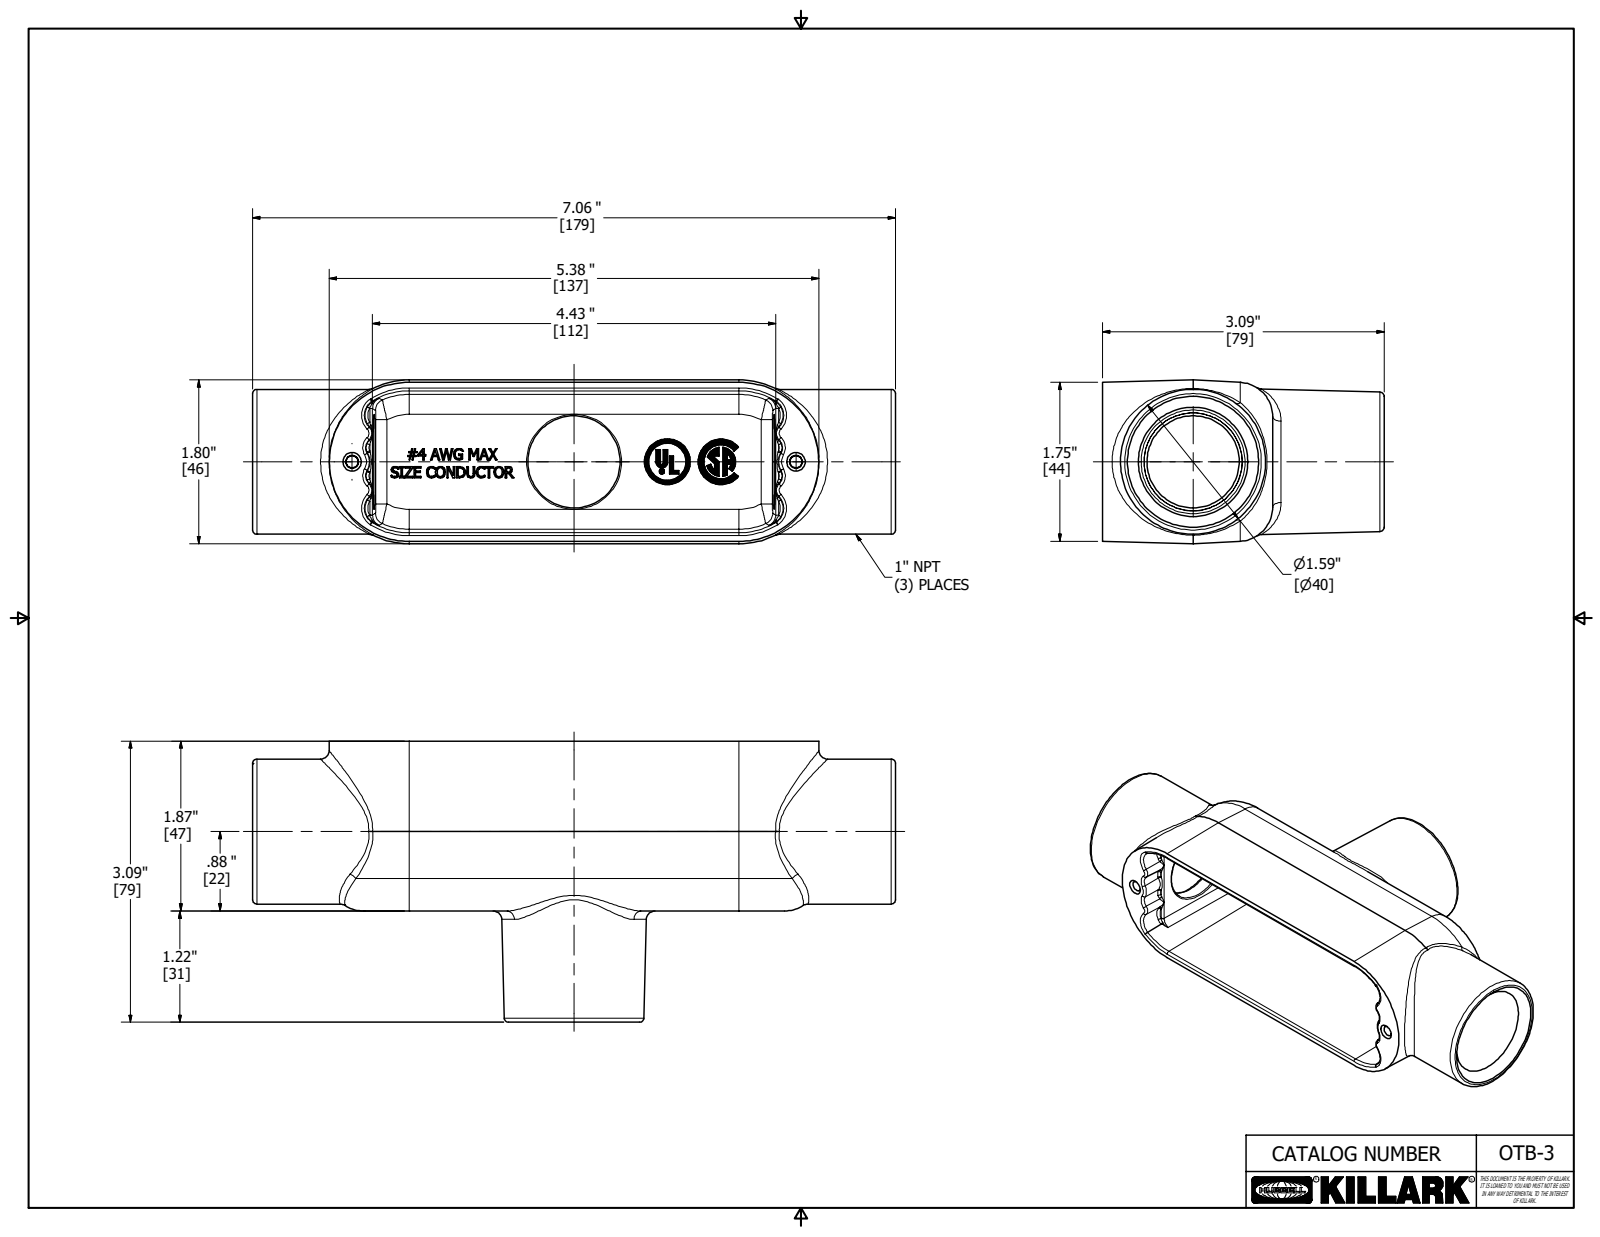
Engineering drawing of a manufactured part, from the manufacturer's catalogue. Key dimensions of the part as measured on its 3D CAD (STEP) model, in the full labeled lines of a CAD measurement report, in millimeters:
Part name (STEP PRODUCT): 12129-1
STEP written by: Autodesk Inventor 2018 (AUTOMOTIVE_DESIGN)
Units: millimetres
Bodies: 1 solid, 778 faces (421 planar, 45 cylindrical, 312 other)
Overall size (bounding box): 179.4 × 78.6 × 45.8
Volume: 104 500 mm³ · Surface area: 53 230 mm²
Round holes (diameter × count): ⌀25.7 ×2, ⌀1.2 ×1, ⌀10.4 ×1
Round bosses / shafts (diameter × count): ⌀40.5 ×1, ⌀12.8 ×1, ⌀1.4 ×1
Partial cylindrical surfaces — rounded edges, fillets, slot ends (radius × count): R0.8 ×8, R0.8 ×4, R3.2 ×2, R5.6 ×2, R9.5 ×2, R0.2 ×1, R0.2 ×1, R0.4 ×1
Main face-to-face distances: 42.1, 2.4, 47.5, 45.1, 0.8, 1.6, 46.7, 1.8, 2.6, 44.9
Hole centre spacings: 3.1, 24.6, 26
